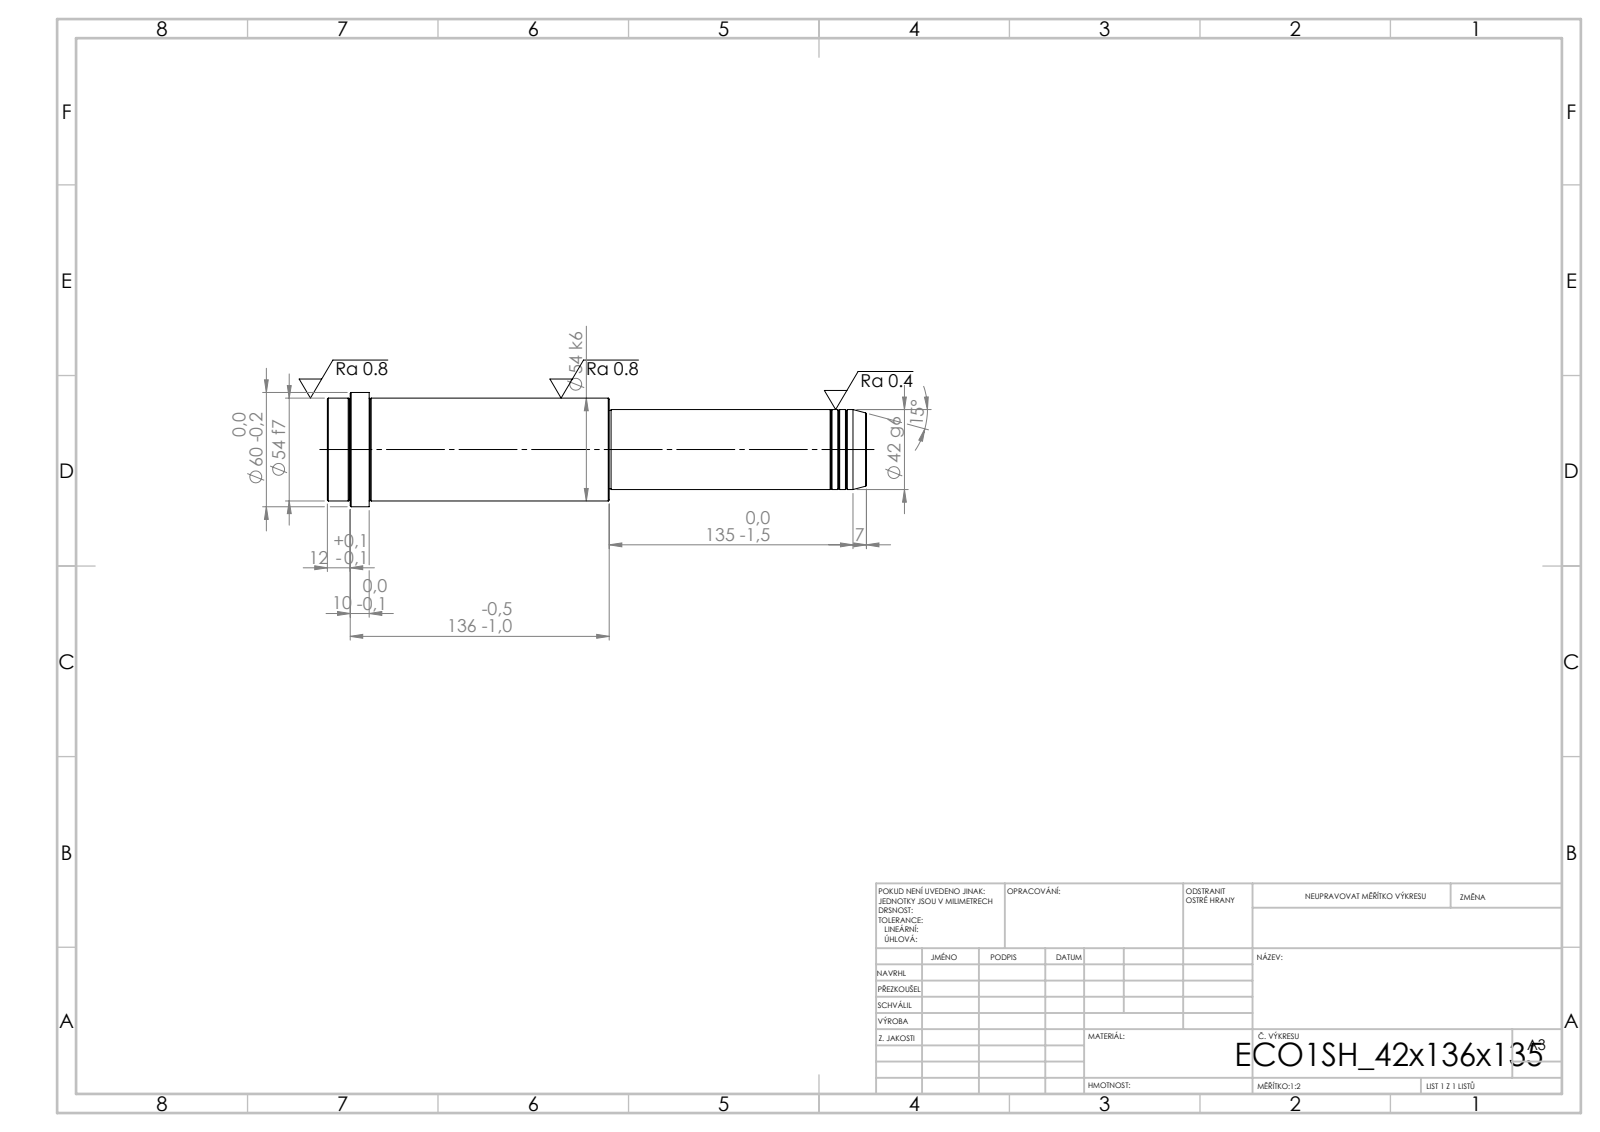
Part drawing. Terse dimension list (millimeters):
written by: SolidWorks 2019 (CONFIG_CONTROL_DESIGN)
unit: mm
bodies: 1 solid, 52 faces (6 planar, 16 cylindrical, 30 other)
size: 283 × 60 × 60
volume: 530 099 mm³; area: 48 879 mm²
bosses: 1× ⌀60, 1× ⌀54, 1× ⌀42, 1× ⌀41
face distances: 283, 135, 148, 261, 126, 22, 271, 136, 10, 12
